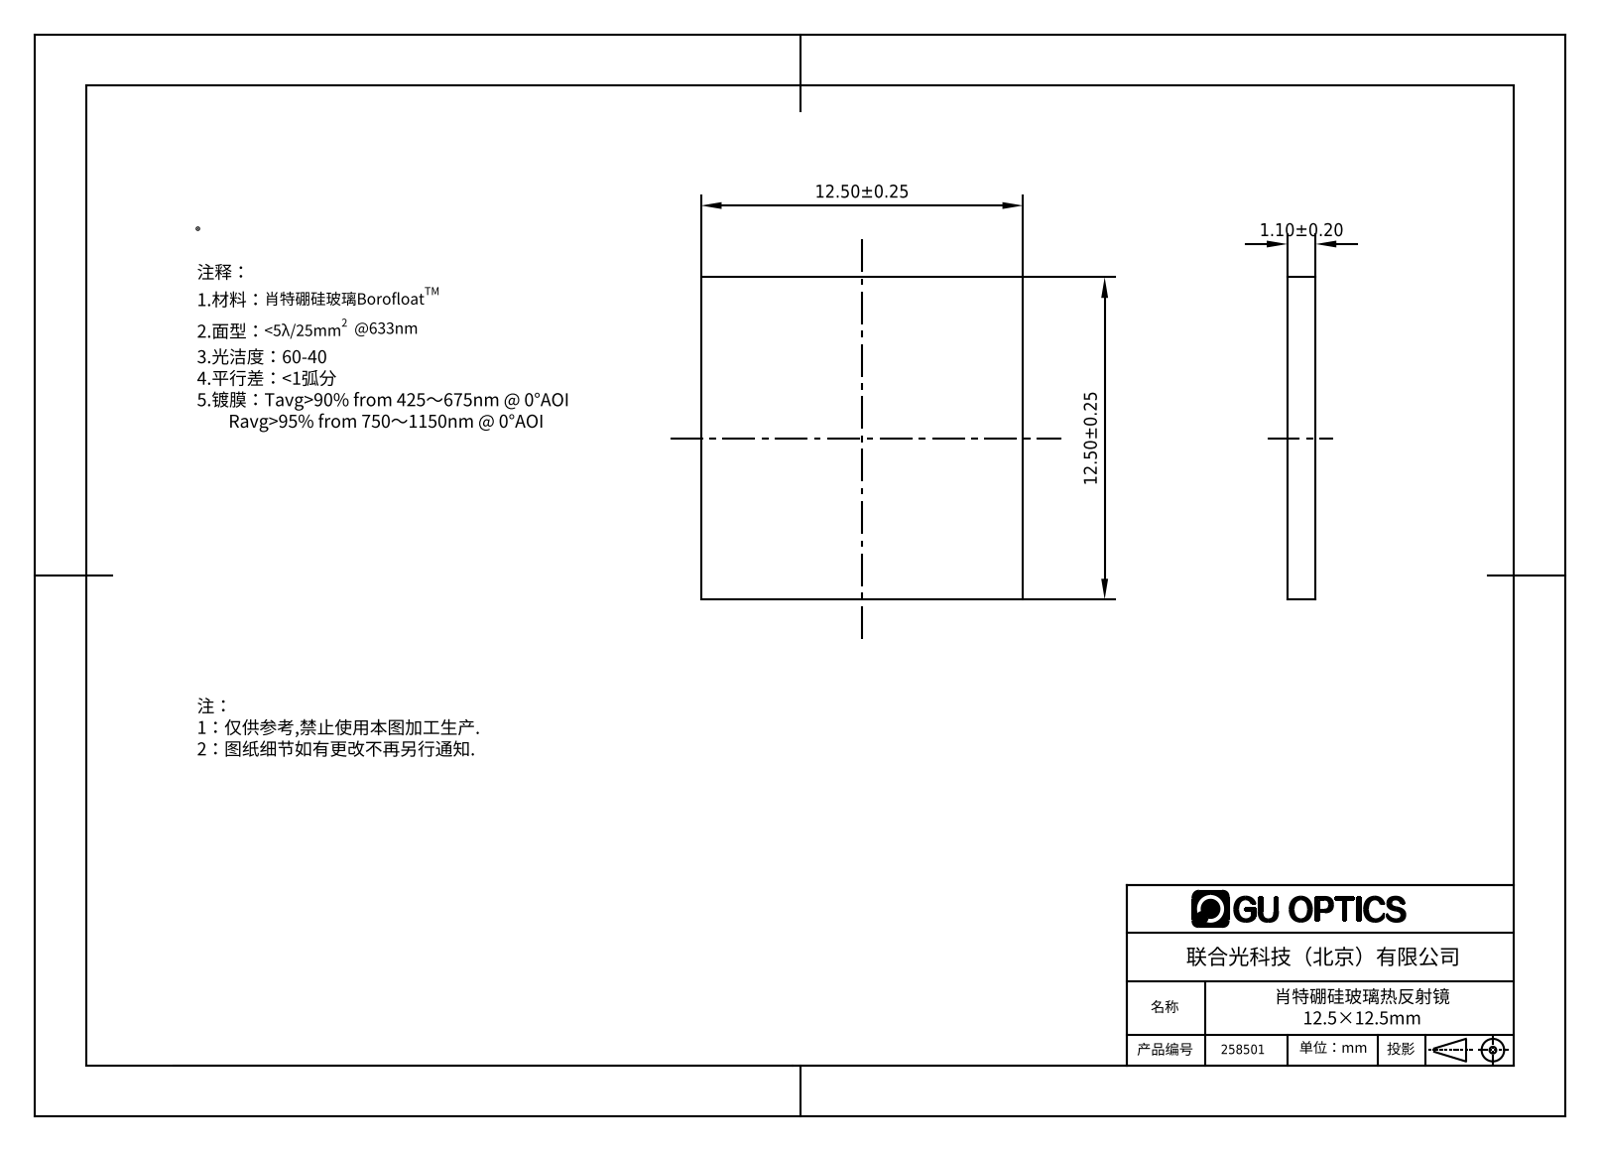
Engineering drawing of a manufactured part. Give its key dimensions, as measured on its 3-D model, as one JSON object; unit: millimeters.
{"part_name": "258501", "step_written_by": "SolidWorks 2016 (AUTOMOTIVE_DESIGN)", "units": "millimeters", "bodies": {"solids": 1, "faces": 6, "planar": 6, "cylindrical": 0, "other": 0}, "overall_size": [12.5, 12.5, 1.1], "volume_mm3": 172, "surface_area_mm2": 368, "face_to_face_distances": [1.1, 12.5]}
